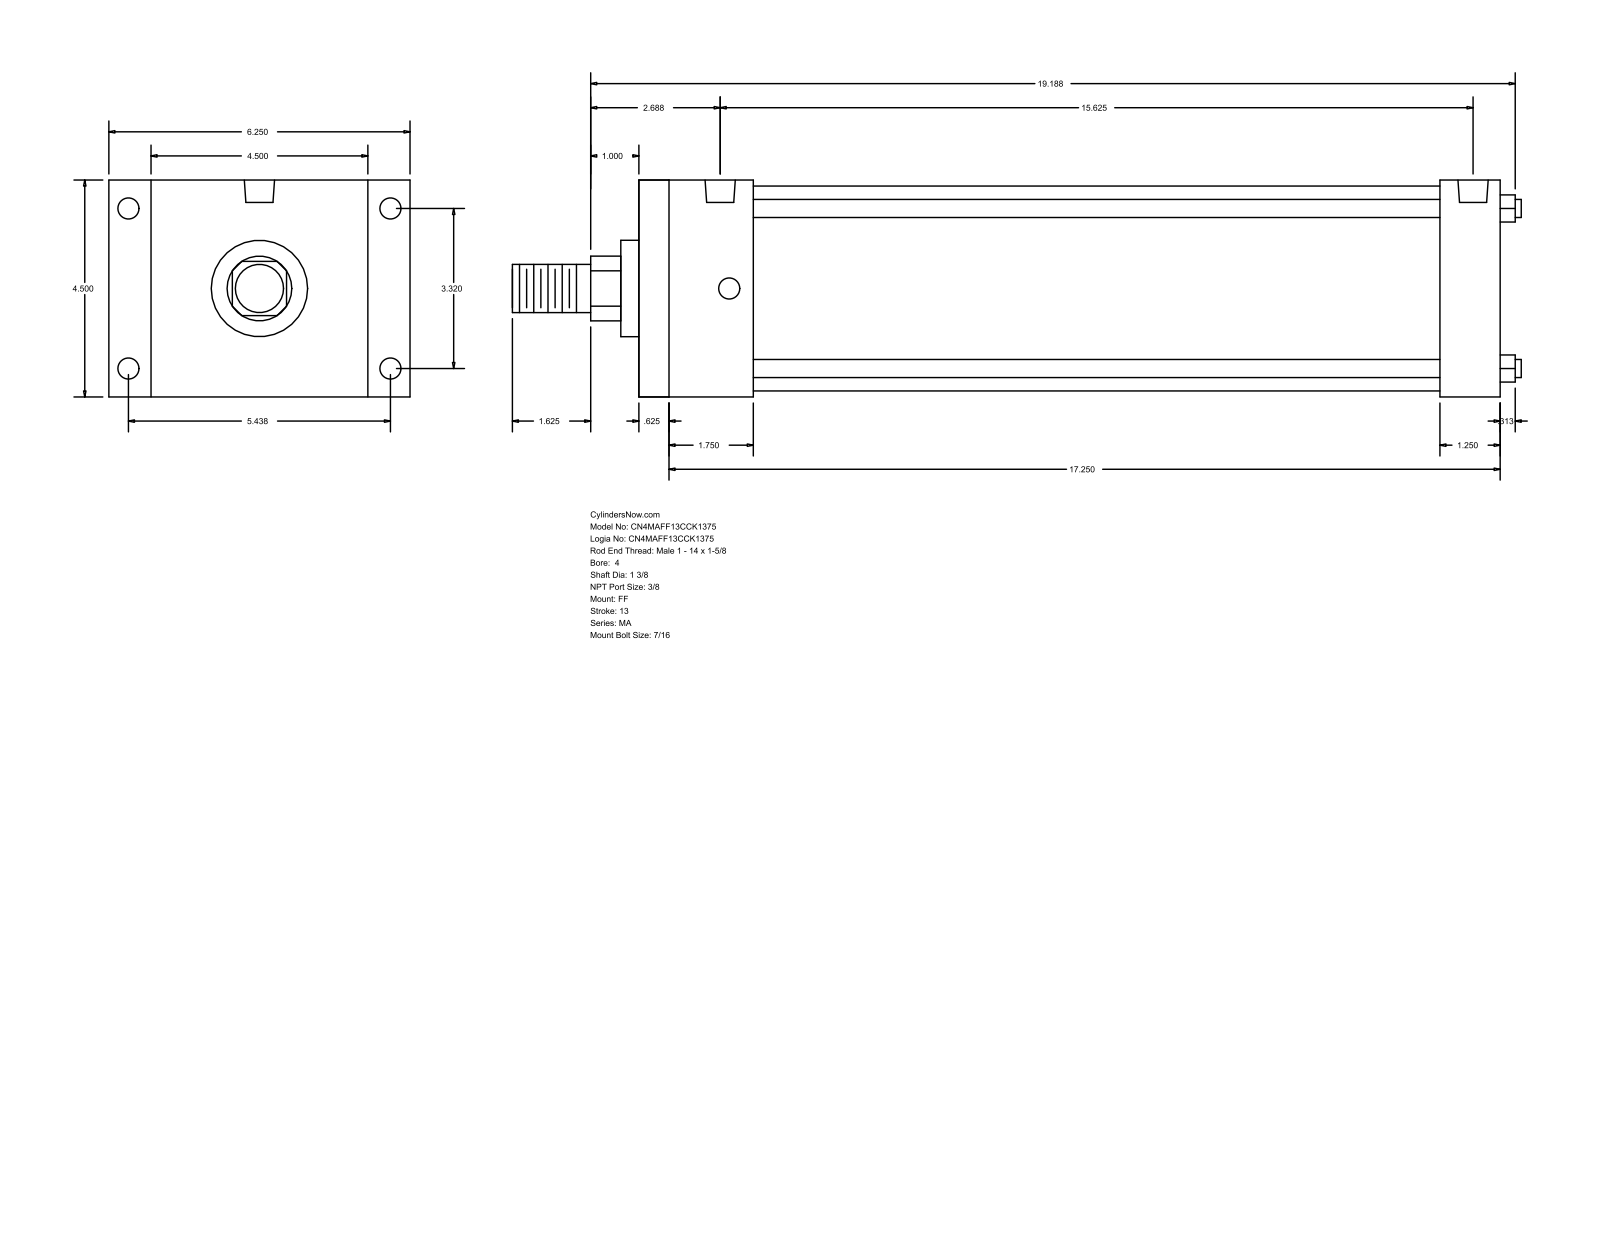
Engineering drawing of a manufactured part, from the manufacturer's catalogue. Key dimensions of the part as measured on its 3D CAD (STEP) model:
Part name (STEP PRODUCT): MA_FF__0400_1.375
STEP written by: GSSL Pune (CONFIG_CONTROL_DESIGN)
Units: millimetres
Bodies: 0 solids, 92 faces (64 planar, 28 cylindrical, 0 other)
Overall size (bounding box): 531.81 × 158.75 × 114.3
Round holes (diameter × count): ⌀11.11 ×8, ⌀15.93 ×2
Round bosses / shafts (diameter × count): ⌀9.53 ×4, ⌀107.95 ×1, ⌀50.8 ×1, ⌀34.92 ×1, ⌀25.4 ×1
Partial cylindrical surfaces — rounded edges, fillets, slot ends (radius × count): R17.06 ×1
Main face-to-face distances: 114.3, 454.03, 15.87, 438.16, 22.23, 136.53, 422.28, 406.41, 31.75, 60.32
Hole centre spacings: 84.32, 138.12, 161.82, 387.35, 4.76, 4.77, 392.11, 392.12
